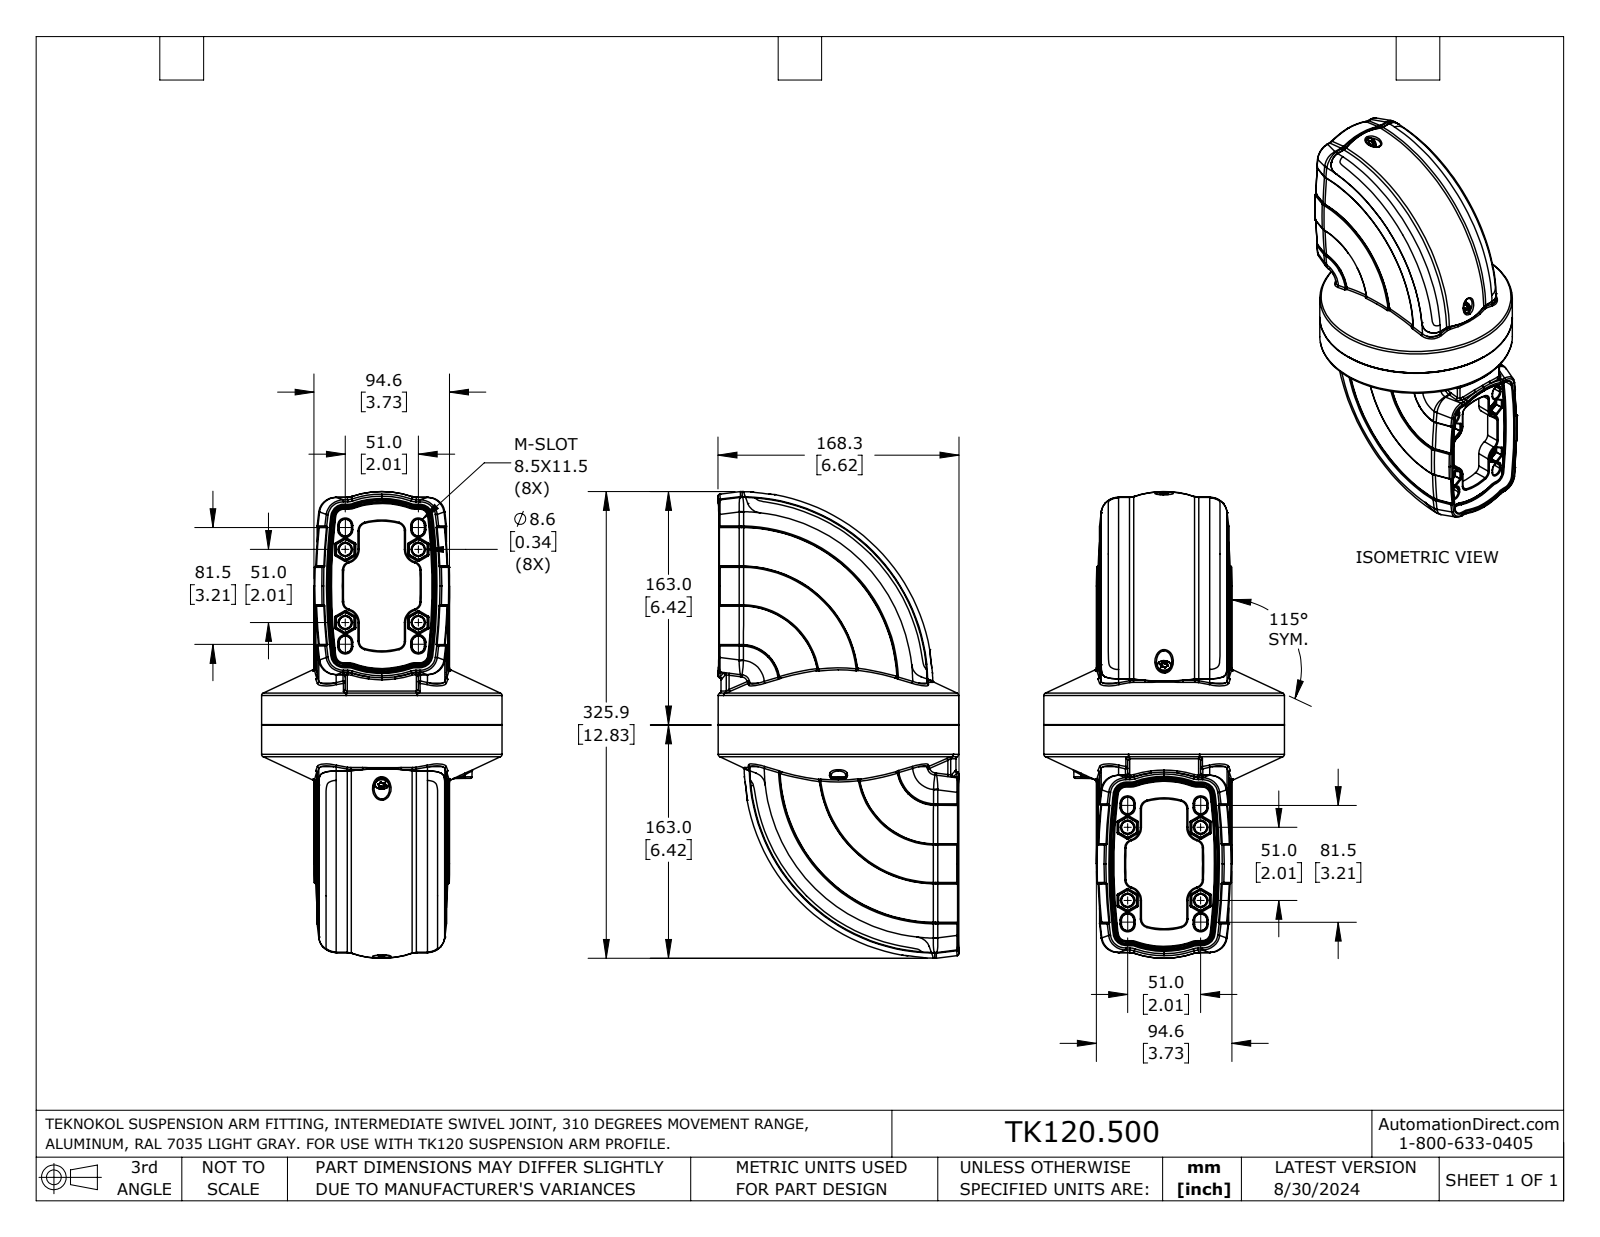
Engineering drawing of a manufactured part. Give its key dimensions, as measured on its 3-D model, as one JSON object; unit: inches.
{"part_name": "TK120.500", "step_written_by": "SolidWorks 2023 (AUTOMOTIVE_DESIGN)", "units": "inches", "bodies": {"solids": 6, "faces": 1606, "planar": 173, "cylindrical": 341, "other": 1092}, "overall_size": [12.832, 6.625, 6.614], "volume_in3": 211.3, "surface_area_in2": 365.2, "round_holes": [[0.197, 1]], "round_bosses_or_shafts": [[0.394, 4], [0.236, 2], [0.236, 2], [6.614, 1]], "partial_cylinders_radius": [[0.01, 88], [0.029, 52], [0.004, 24], [0.108, 24], [0.209, 16], [0.055, 8], [0.381, 8], [0.059, 4]], "face_to_face_distances": [0.551, 0.482, 5.335, 0.276, 4.853, 5.817, 2.008, 1.004, 6.624, 1.246]}
